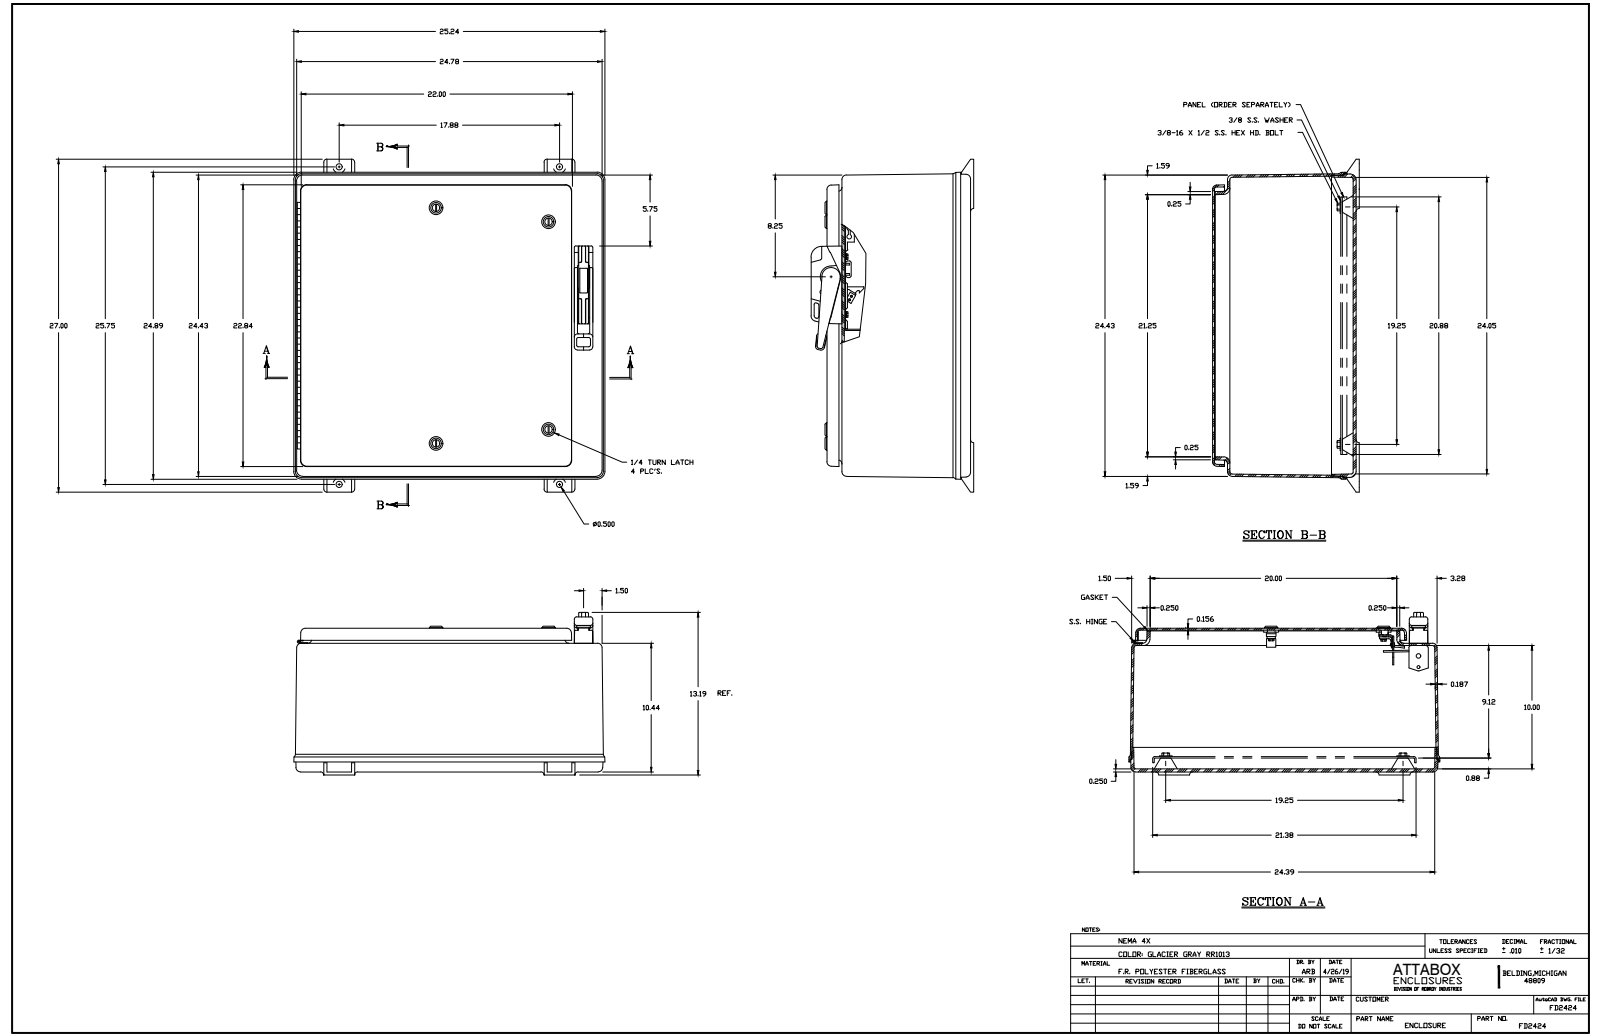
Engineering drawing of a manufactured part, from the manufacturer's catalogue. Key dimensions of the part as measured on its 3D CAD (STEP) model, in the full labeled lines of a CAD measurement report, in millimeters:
Part name (STEP PRODUCT): FD2424
STEP written by: SolidWorks 2018 (AUTOMOTIVE_DESIGN)
Units: millimetres
Bodies: 88 solids, 2573 faces (1270 planar, 735 cylindrical, 568 other)
Overall size (bounding box): 685.8 × 641.4 × 335
Volume: 9 634 000 mm³ · Surface area: 4 184 000 mm²
Round holes (diameter × count): ⌀3.8 ×12, ⌀4.7 ×8, ⌀12.7 ×8, ⌀6.5 ×5, ⌀4.3 ×4, ⌀5.5 ×4, ⌀7.1 ×4, ⌀7.8 ×4, ⌀7.9 ×4, ⌀11 ×4, ⌀14.3 ×4, ⌀16 ×4
Round bosses / shafts (diameter × count): ⌀7.6 ×8, ⌀5.1 ×6, ⌀27.8 ×4, ⌀25.4 ×4, ⌀16 ×4, ⌀9.5 ×4, ⌀9.1 ×4, ⌀7 ×4
Partial cylindrical surfaces — rounded edges, fillets, slot ends (radius × count): R6.4 ×37, R3.2 ×19, R4 ×17, R4.8 ×16, R8 ×12, R12.7 ×12, R7.9 ×10, R9.5 ×10
Main face-to-face distances: 4.7, 6.4, 296, 289.7, 4, 292, 285.7, 25.5, 3.3, 28.6
Hole centre spacings: 157.1, 7.1, 0.4, 163.9, 219.3, 269.7, 314.2, 427.8
